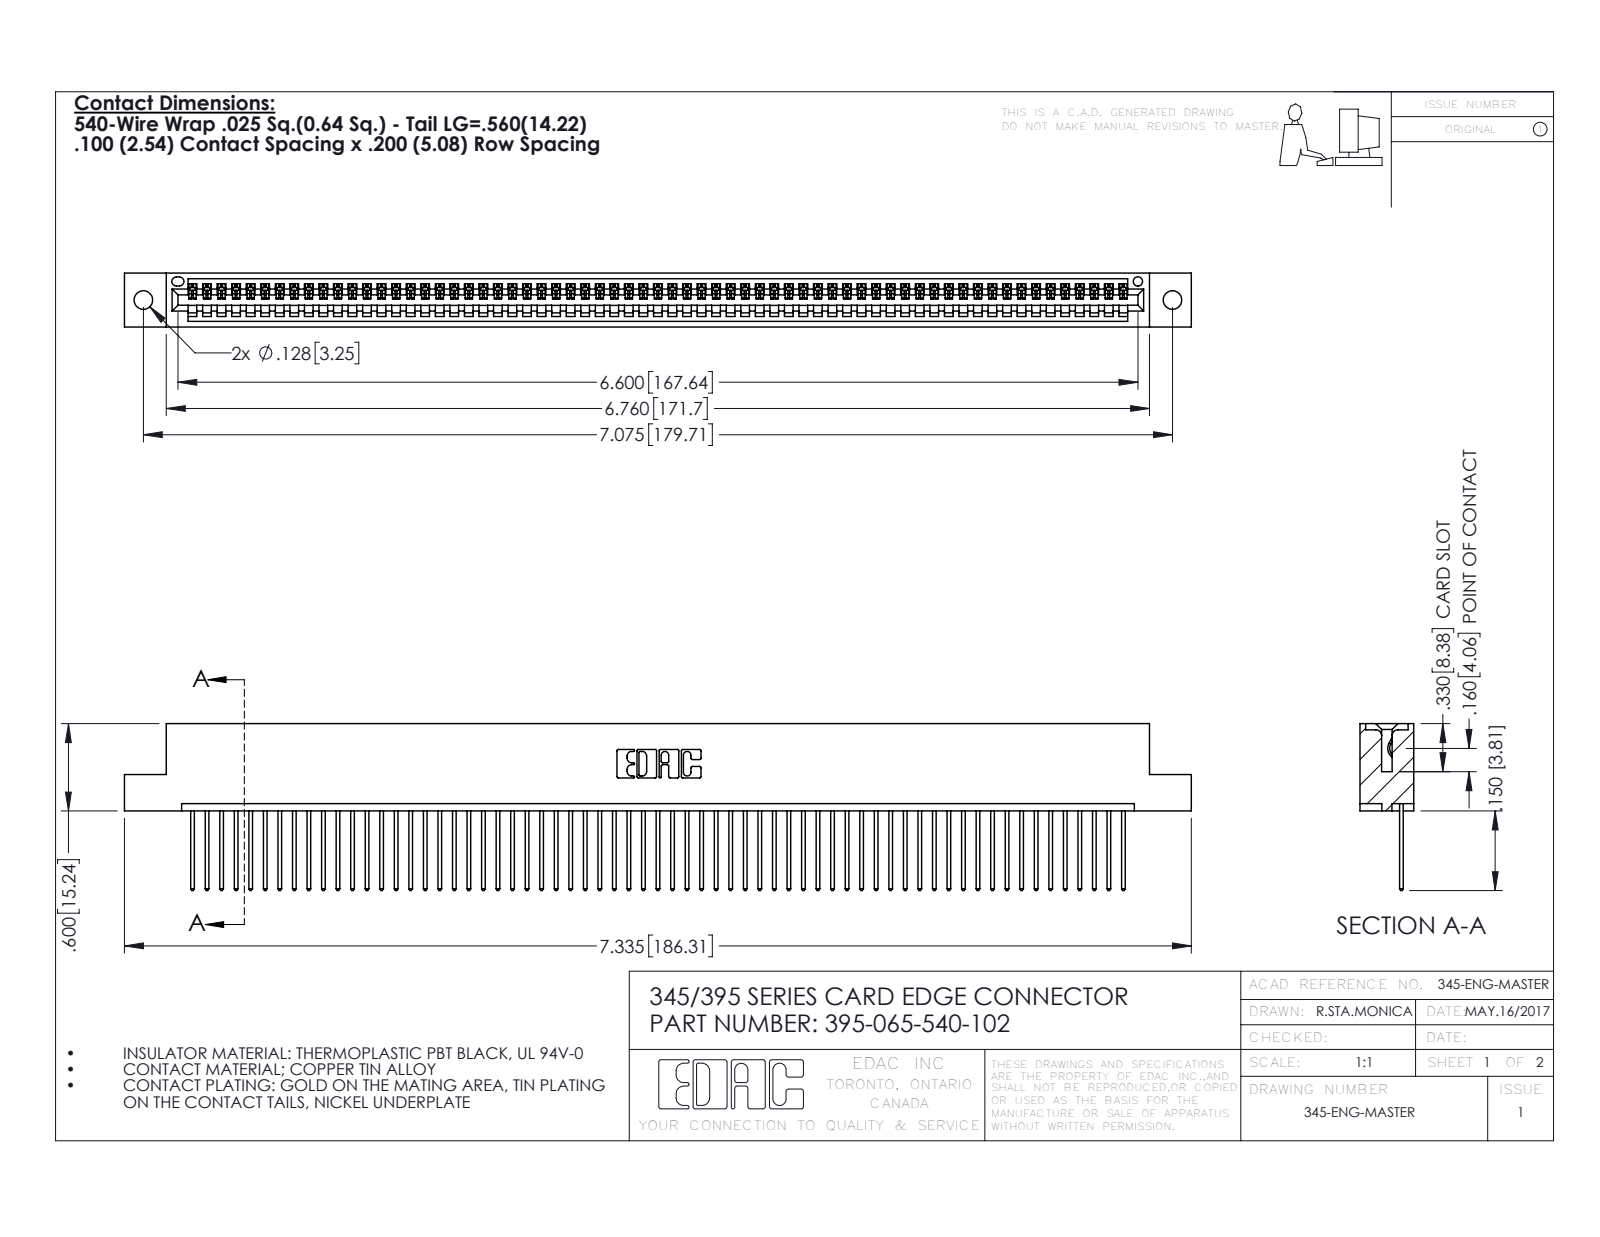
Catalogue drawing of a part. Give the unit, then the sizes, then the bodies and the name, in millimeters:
Units: millimetres
Overall size (bounding box): 186.3 × 29.1 × 9.4
Round holes (diameter × count): ⌀3.3 ×2, ⌀1.6 ×1
Partial cylindrical surfaces — rounded edges, fillets, slot ends (radius × count): R0.2 ×130, R0.3 ×130, R0.3 ×22, R0.2 ×6, R0.8 ×6, R0.7 ×3, R0.8 ×2, R1 ×2
Main face-to-face distances: 7.6, 1.8, 9.4, 2.5, 6.9, 0.6, 5.1, 5.7, 3.8, 1.8
Hole centre spacings: 6.9, 173.7, 179.7
Volume: 17 930 mm³ · Surface area: 24 510 mm²
Bodies: 66 solids, 3896 faces (2680 planar, 1216 cylindrical, 0 other)
Part name (STEP PRODUCT): 345 Part_Flush Mounting Lugs - 0.128 Dia; 345-292-001_345-293-140; 395-065-540-102
STEP written by: SolidWorks 2016 (CONFIG_CONTROL_DESIGN)
